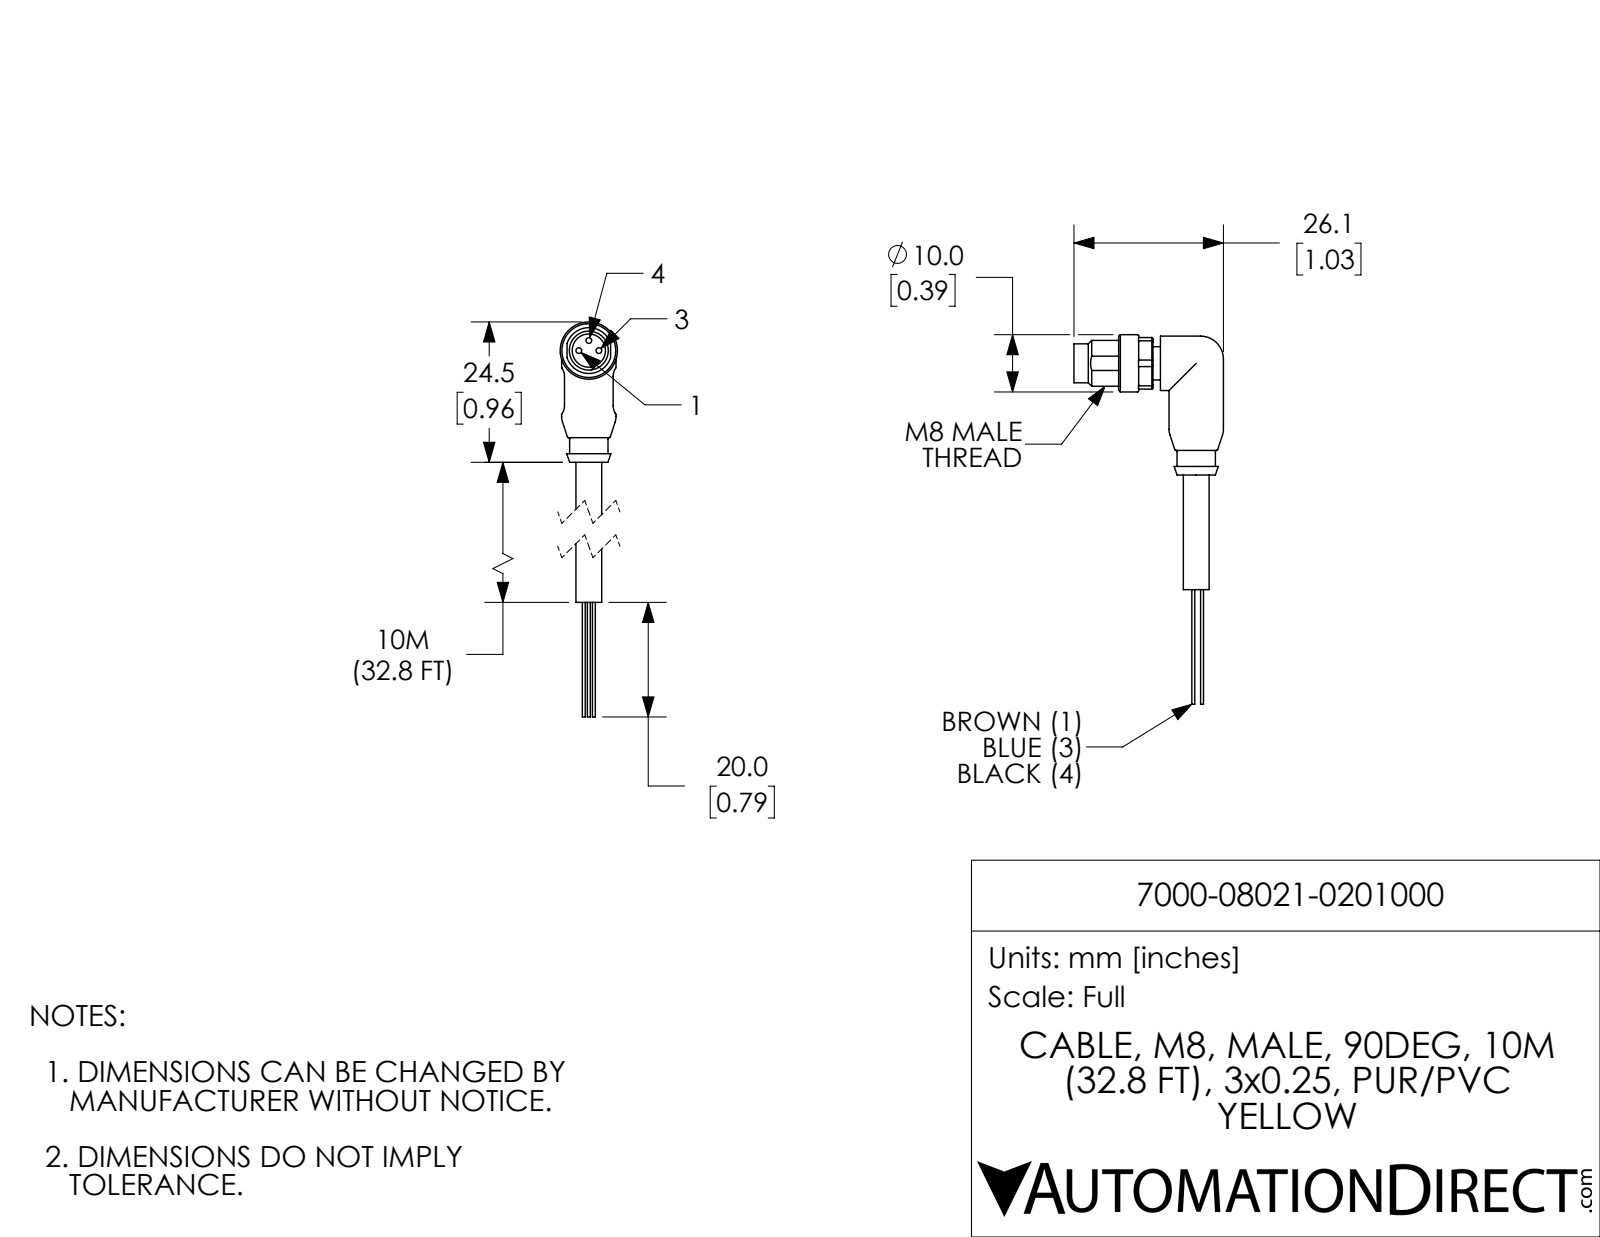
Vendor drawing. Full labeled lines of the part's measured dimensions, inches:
Part name (STEP PRODUCT): 7000-08021-0201000
STEP written by: SolidWorks 2017 (AUTOMOTIVE_DESIGN)
Units: inches
Bodies: 4 solids, 118 faces (40 planar, 45 cylindrical, 33 other)
Overall size (bounding box): 2.539 × 1.028 × 0.394
Volume: 0.161 in³ · Surface area: 2.831 in²
Round holes (diameter × count): ⌀0.228 ×1
Round bosses / shafts (diameter × count): ⌀0.039 ×3, ⌀0.02 ×3, ⌀0.374 ×2, ⌀0.394 ×1, ⌀0.315 ×1, ⌀0.268 ×1, ⌀0.264 ×1, ⌀0.177 ×1
Partial cylindrical surfaces — rounded edges, fillets, slot ends (radius × count): R0.008 ×4, R0.098 ×4, R0.193 ×1
Main face-to-face distances: 0.051, 0.354, 0.018, 0.317, 0.346, 0.398, 0.335, 0.11, 0.236, 0.287
